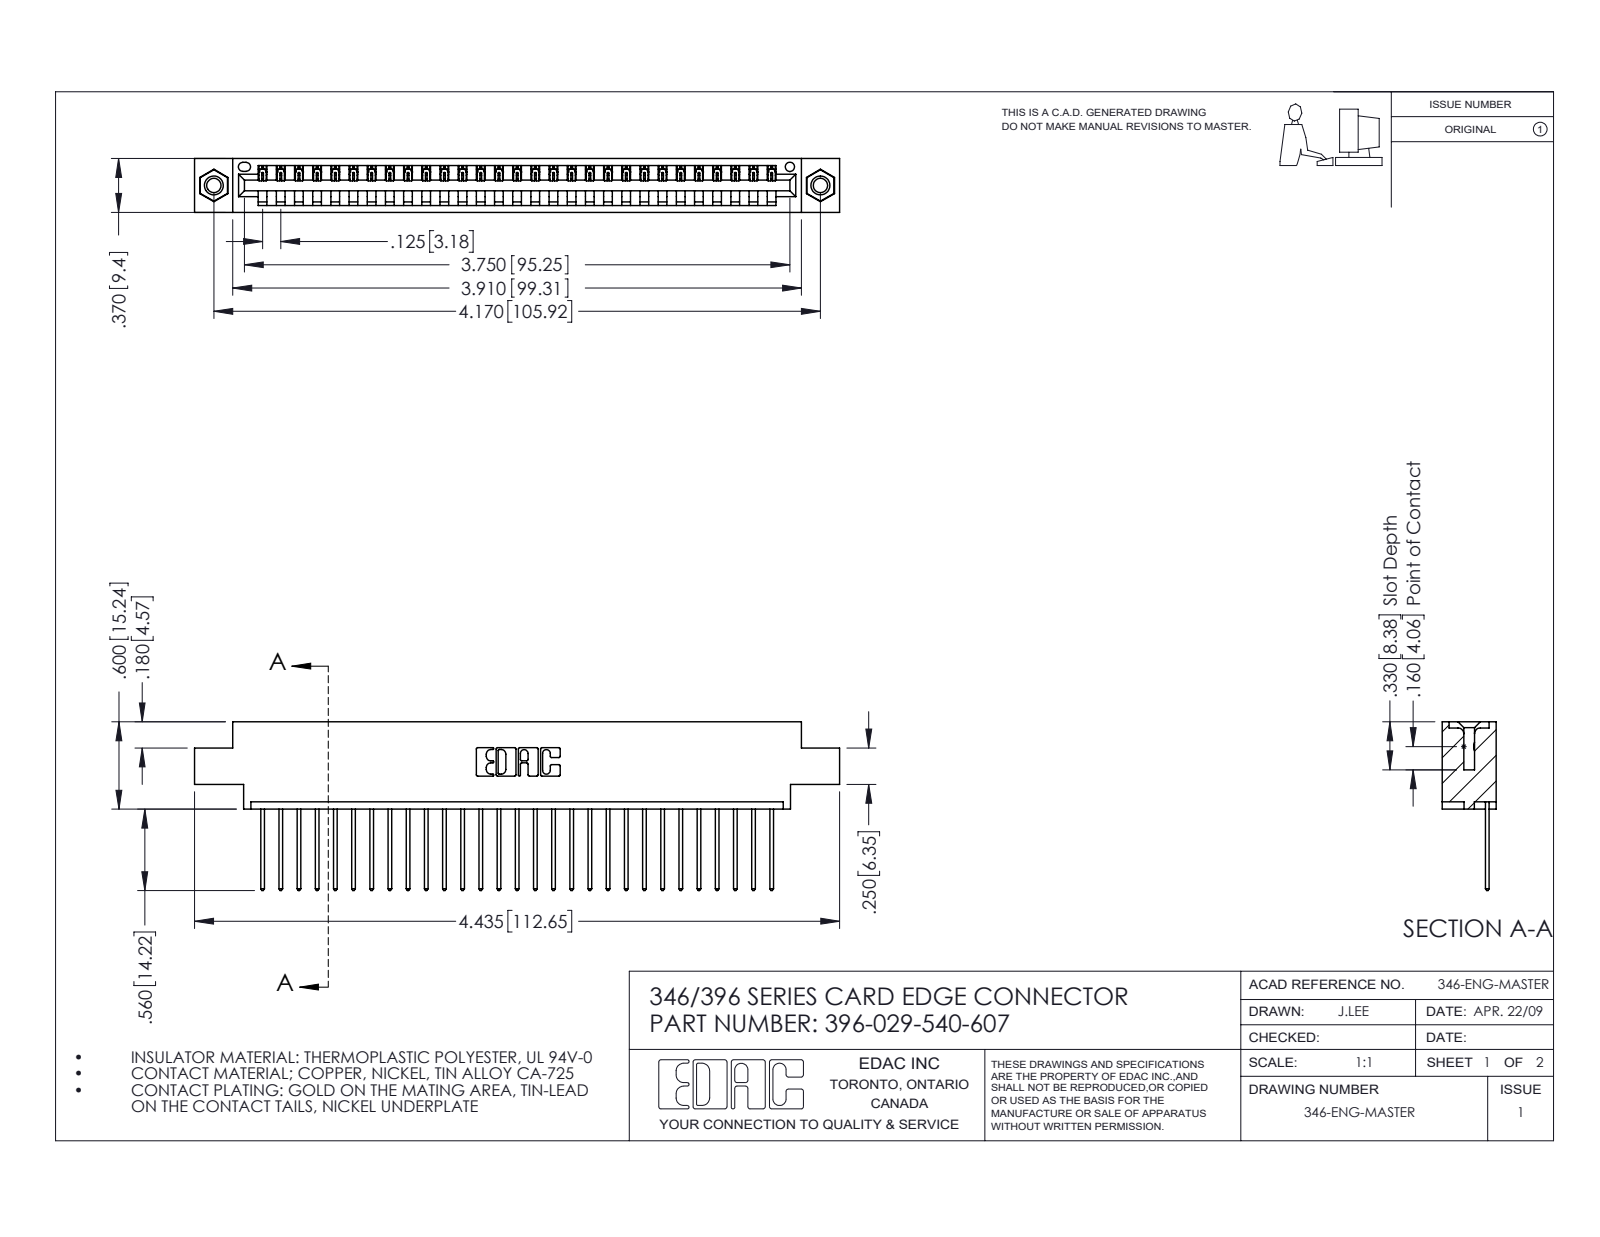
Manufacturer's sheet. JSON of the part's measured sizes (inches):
{"part_name": "345-292-001_345-293-140; 396-029-540-607; 346 Part_0.170 Offset - 0.156 Dia-TI; 345-250-001_345-250-005-103", "step_written_by": "SolidWorks 2016 (CONFIG_CONTROL_DESIGN)", "units": "inches", "bodies": {"solids": 32, "faces": 1868, "planar": 1272, "cylindrical": 580, "other": 16}, "overall_size": [4.435, 1.16, 0.37], "volume_in3": 0.645, "surface_area_in2": 21, "round_holes": [[0.098, 2], [0.125, 2], [0.156, 2], [0.064, 1]], "round_bosses_or_shafts": [[0.155, 2]], "partial_cylinders_radius": [[0.006, 58], [0.01, 58], [0.01, 22], [0.007, 6], [0.031, 6], [0.026, 3], [0.031, 2], [0.04, 2]], "face_to_face_distances": [0.048, 0.322, 0.37, 0.25, 0.072, 0.298, 0.025, 0.222, 0.148, 0.1], "hole_center_spacings": [0.246, 3.962, 4.17]}
